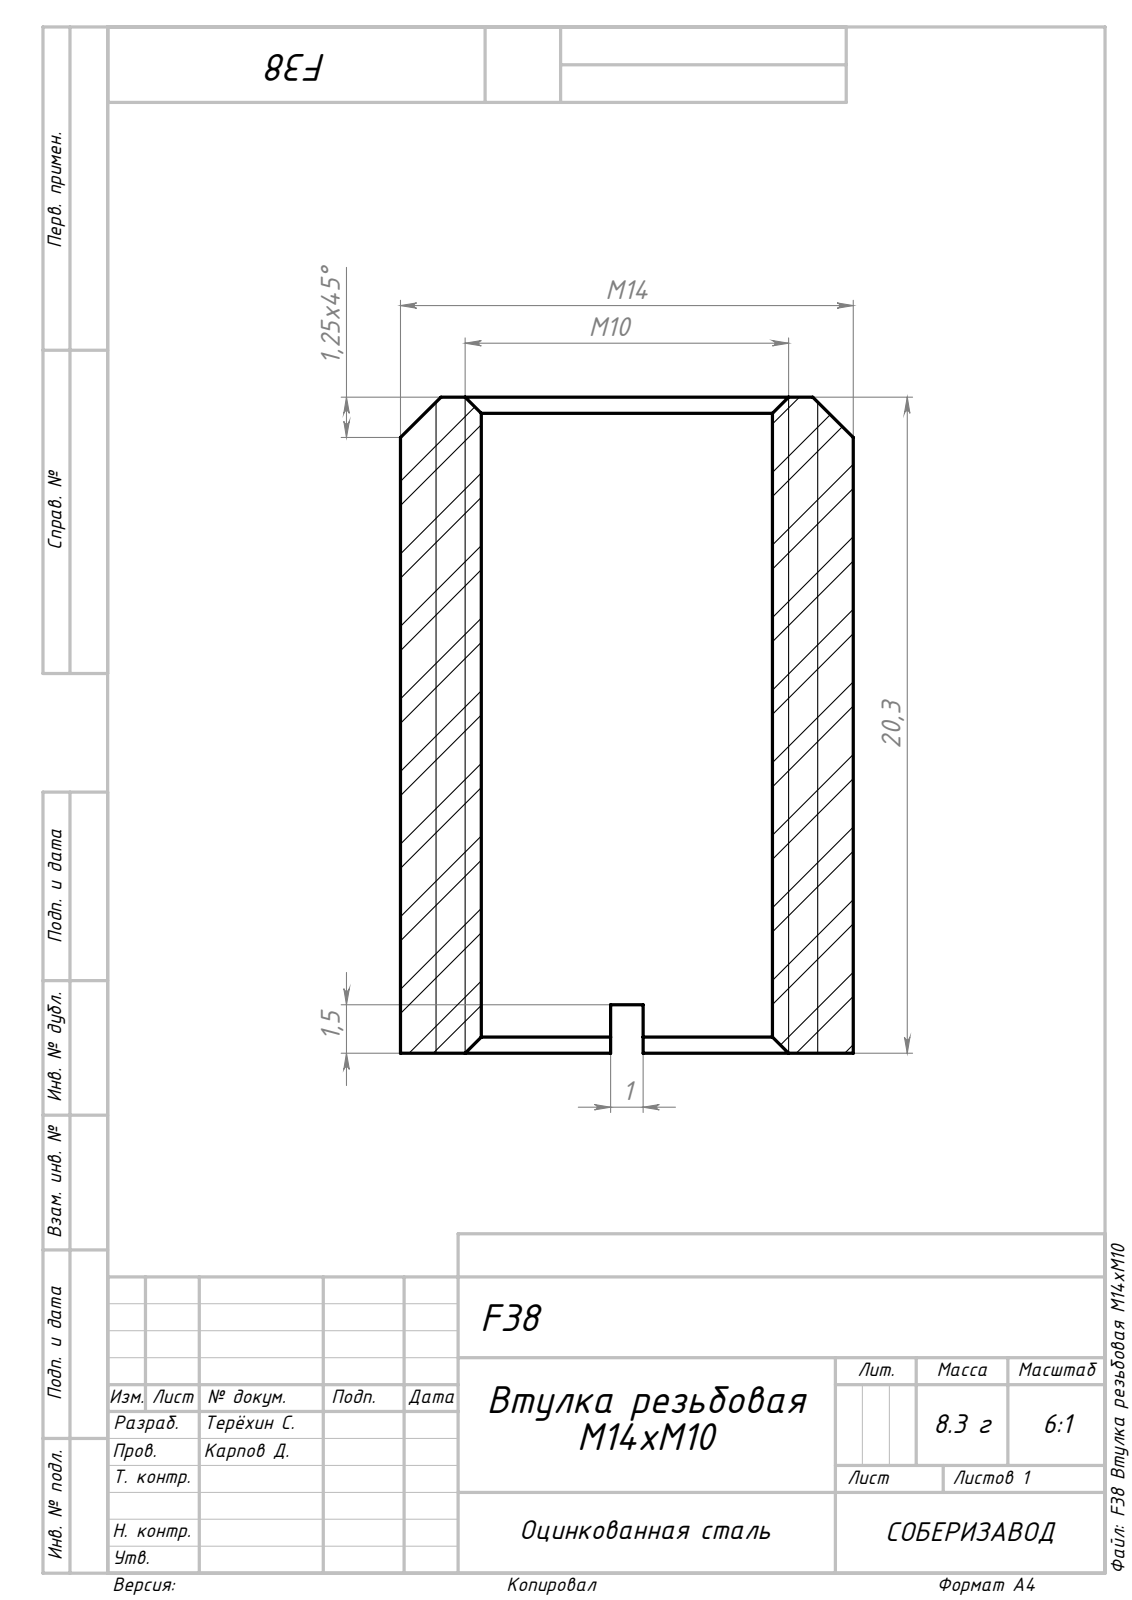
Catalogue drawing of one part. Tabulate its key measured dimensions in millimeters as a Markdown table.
| quantity | value |
| --- | --- |
| STEP written by | SolidWorks 2018 (AUTOMOTIVE_DESIGN) |
| units | millimeters |
| bodies | 1 solid, 19 faces (9 planar, 4 cylindrical, 6 other) |
| overall size | 20.3 × 14 × 14 |
| volume | 1 787 mm³ |
| surface area | 1 606 mm² |
| round holes (diameter × count) | 9 × 1 |
| round bosses / shafts (diameter × count) | 14 × 1 |
| main face-to-face distances | 20.3, 1, 1.5, 18.8 |
